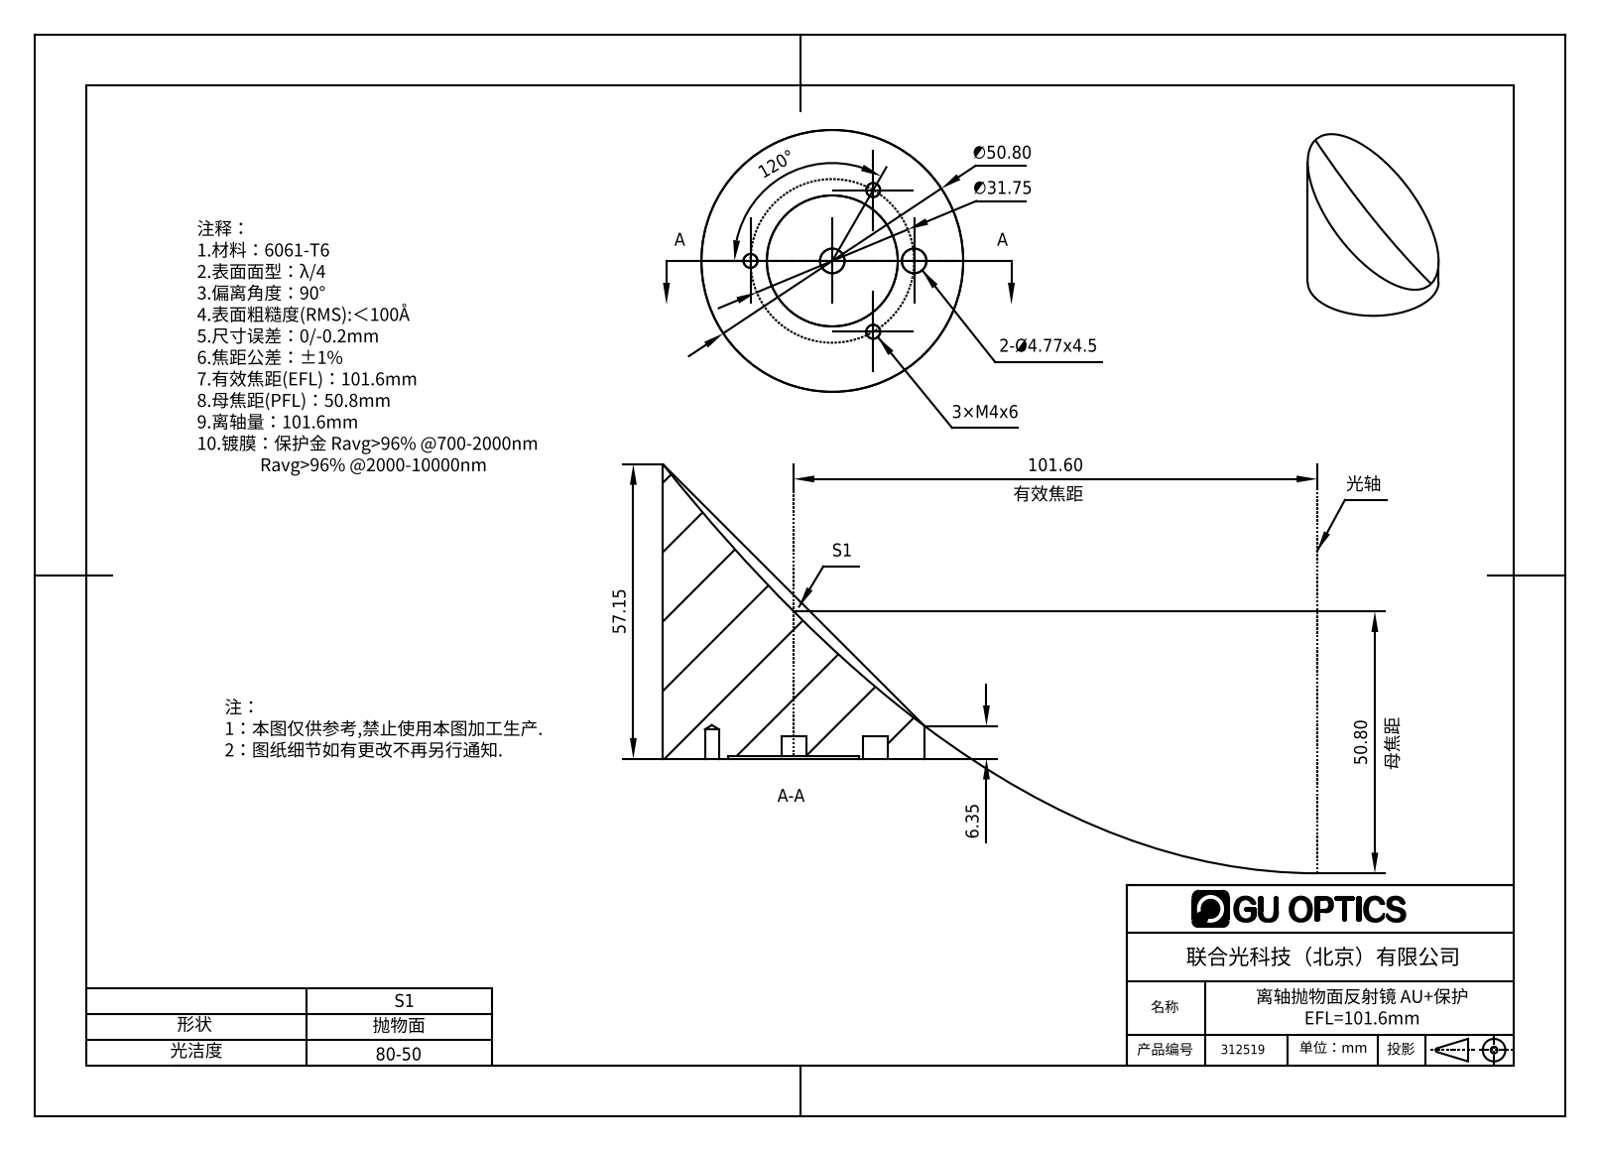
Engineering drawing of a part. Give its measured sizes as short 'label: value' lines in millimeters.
name: Ø50_36596
written by: SolidWorks 2018 (CONFIG_CONTROL_DESIGN)
unit: mm
bodies: 1 solid, 26 faces (4 planar, 14 cylindrical, 8 other)
size: 57.15 × 50.8 × 50.8
volume: 60 628 mm³; area: 10 288 mm²
holes: 3× ⌀2.71, 1× ⌀4.77, 1× ⌀4.78, 1× ⌀25.4
bosses: 1× ⌀50.8
face distances: 0.51, 4.32, 3.81
hole spacings: 15.88, 27.5, 31.76
